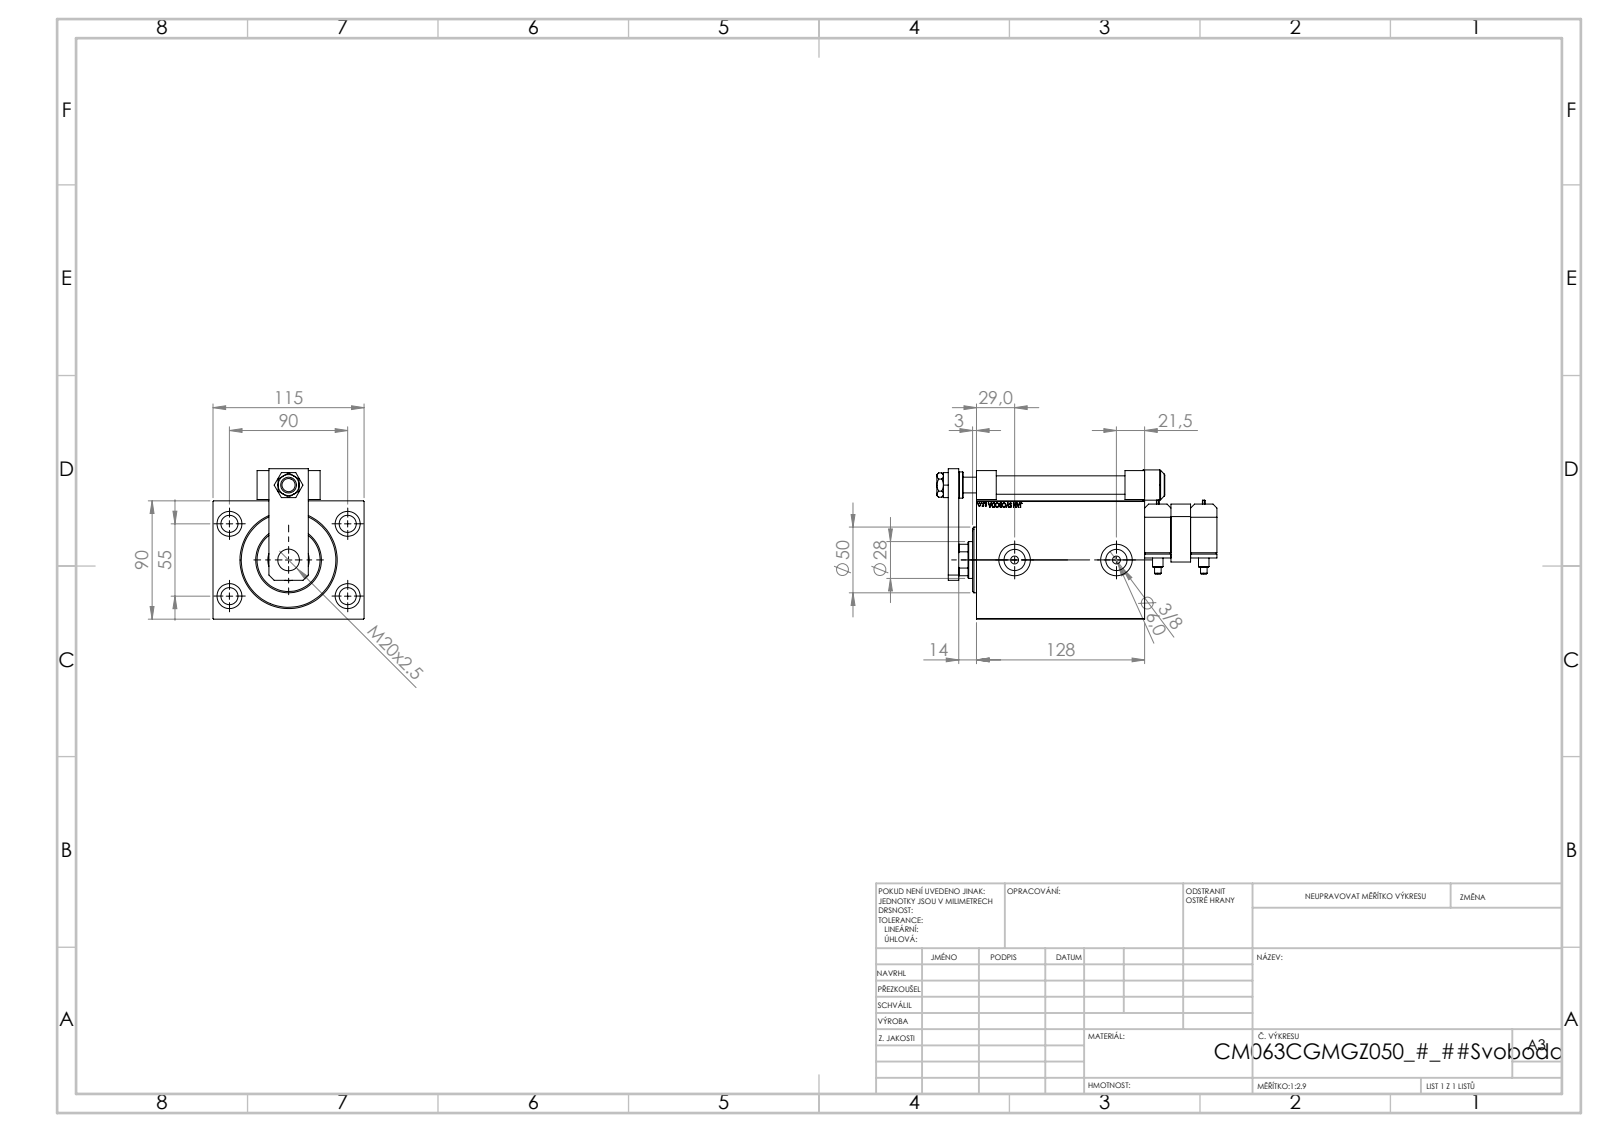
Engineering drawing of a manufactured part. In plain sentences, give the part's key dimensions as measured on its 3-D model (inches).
The part is named "SWITCH P; SWITCH_P_FRONT_BACK; SWITCH DIM W_B; TYC_P (+7 more)". Its 3-D file was written by "SolidWorks 2019 (CONFIG_CONTROL_DESIGN)". It is 14 solids with 1118 faces: 525 planar, 128 cylindrical and 465 other. Overall it measures 8.394 by 4.528 by 4.508 inches. Its volume is 78.11 cubic inches and its surface area 315.9 square inches. Round holes: 5 of diameter 0.512, 4 of diameter 0.157, 4 of diameter 0.315, 4 of diameter 0.748, 2 of diameter 0.236, 2 of diameter 0.637, 2 of diameter 0.945, 1 of diameter 0.472, 1 of diameter 0.551, 1 of diameter 0.65, 1 of diameter 0.728, 1 of diameter 1.102. Round bosses or shafts: 3 of diameter 0.787, 2 of diameter 0.63, 2 of diameter 0.551, 2 of diameter 0.315, 2 of diameter 0.236, 2 of diameter 0.198, 1 of diameter 1.969, 1 of diameter 0.906. Partial cylindrical surfaces (rounded edges, fillets, slot ends): 1 of radius 0.118, 1 of radius 0.531. The main face-to-face distances are 3.543, 4.528, 1.378, 5.039, 0.689, 4.35, 1.476, 0.531, 5.886, 0.591. The hole center spacings are 2.076, 0.787, 2.119, 2.165, 3.543, 3.769, 4.153, 4.449.
